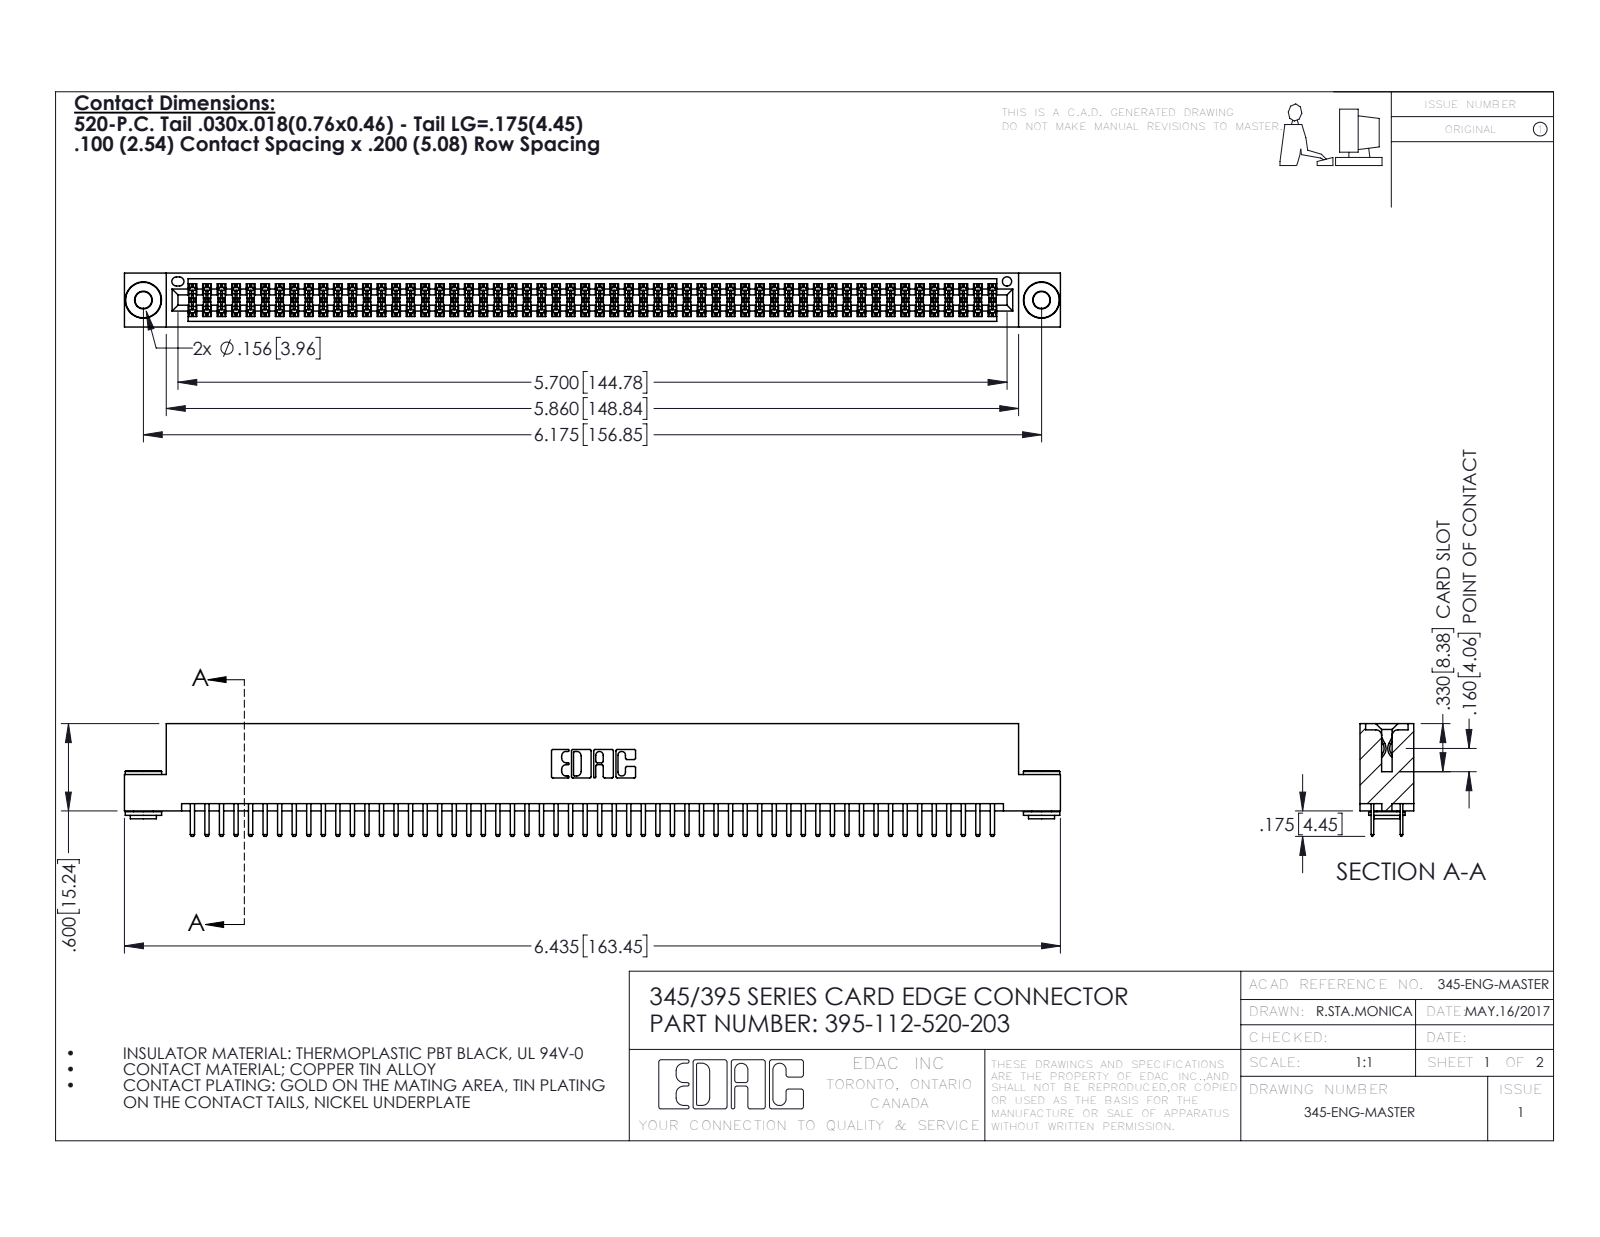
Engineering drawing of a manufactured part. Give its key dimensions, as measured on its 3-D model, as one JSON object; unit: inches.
{"part_name": "345 Part_Flush Mounting Lugs - 0.156 Dia-TH; 345-250-002_345-250-002-102; 395-112-520-203; 345-292-001_345-293-120", "step_written_by": "SolidWorks 2016 (CONFIG_CONTROL_DESIGN)", "units": "inches", "bodies": {"solids": 115, "faces": 6212, "planar": 4010, "cylindrical": 2194, "other": 8}, "overall_size": [6.435, 0.775, 0.37], "volume_in3": 0.975, "surface_area_in2": 37.18, "round_holes": [[0.116, 2], [0.156, 2], [0.064, 1]], "round_bosses_or_shafts": [[0.25, 2], [0.18, 2], [0.136, 2]], "partial_cylinders_radius": [[0.006, 168], [0.01, 116], [0.01, 22], [0.007, 6], [0.031, 6], [0.026, 3], [0.014, 2], [0.019, 2]], "face_to_face_distances": [0.072, 0.298, 0.2, 0.37, 0.025, 0.098, 0.272, 0.225, 0.022, 0.072], "hole_center_spacings": [0.27, 5.939, 6.175]}
